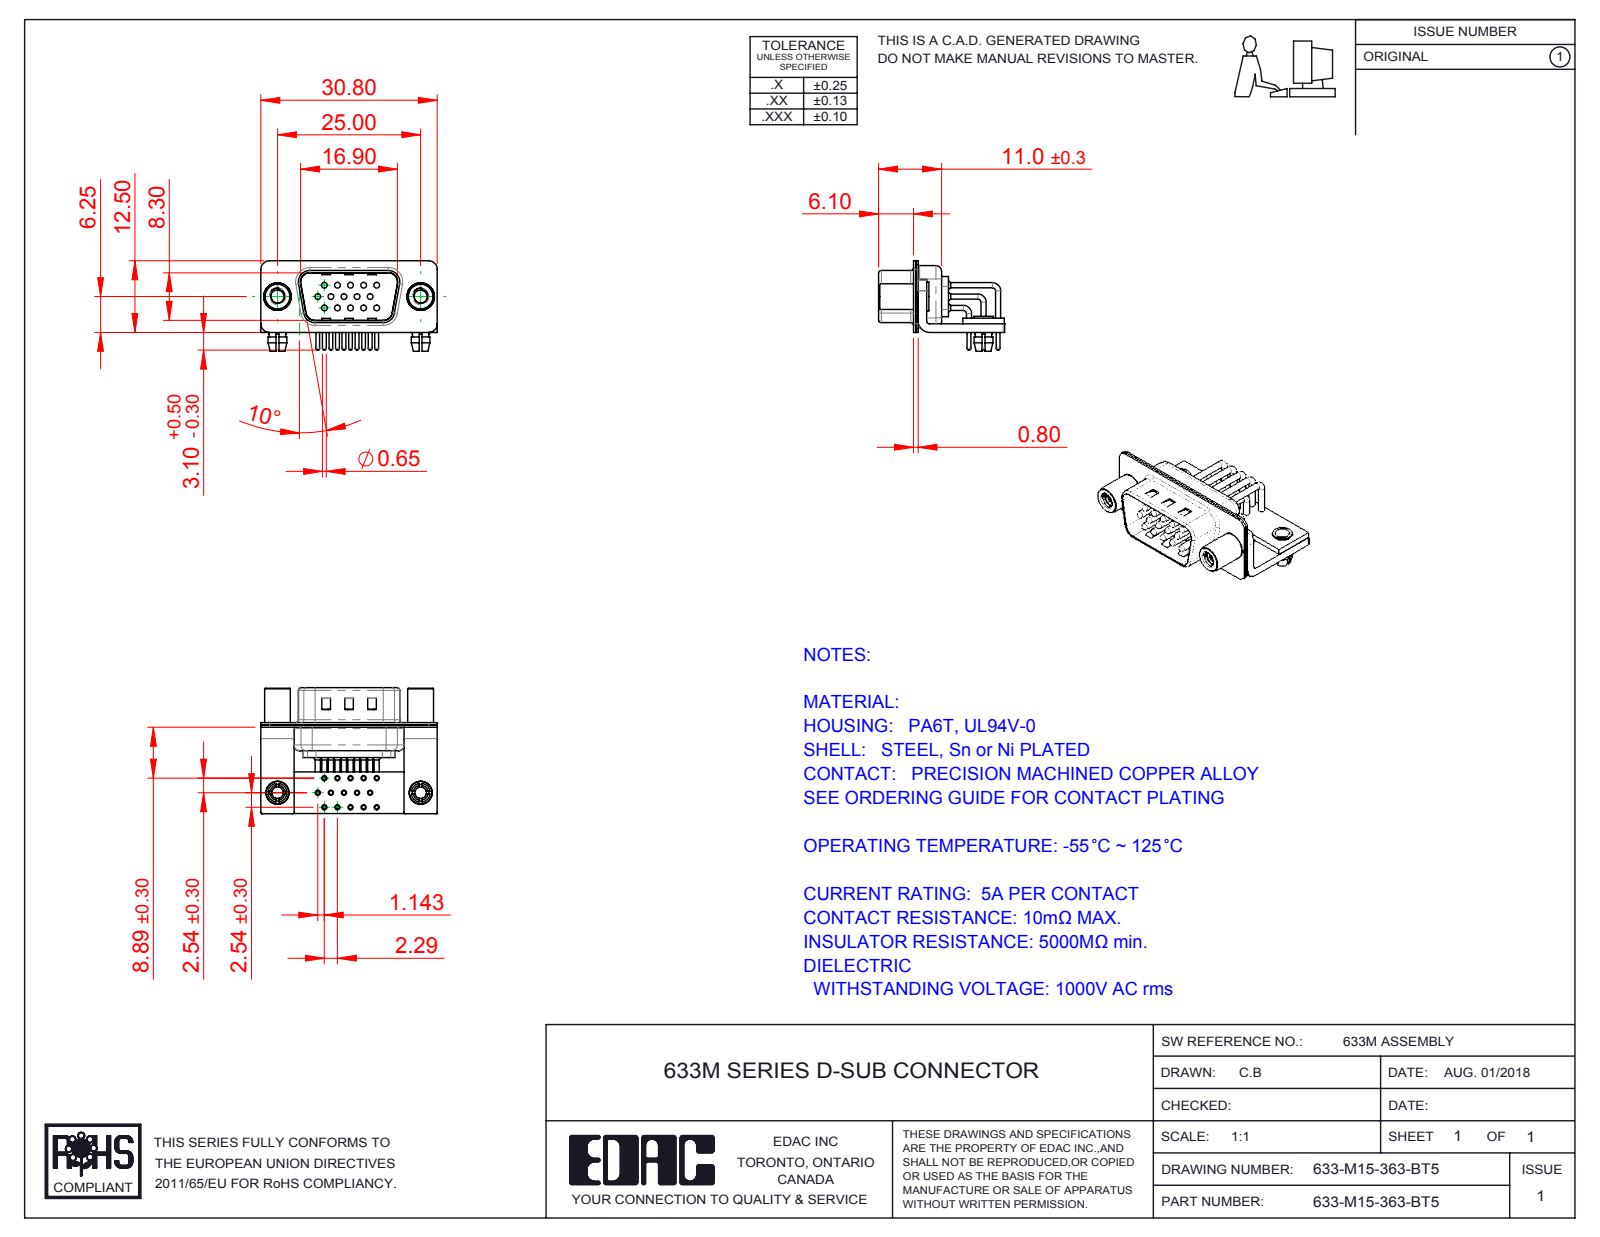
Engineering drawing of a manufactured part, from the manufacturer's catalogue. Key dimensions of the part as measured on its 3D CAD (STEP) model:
Part name (STEP PRODUCT): 633M Shell Front_15 Contacts; 633M Contact Row 3; 633M Shell Rear_15 Contacts; 633M Stabilizer Bracket (+7 more)
STEP written by: SolidWorks 2016 (CONFIG_CONTROL_DESIGN)
Units: millimetres
Bodies: 25 solids, 2176 faces (1143 planar, 795 cylindrical, 238 other)
Overall size (bounding box): 30.8 × 22 × 15.8
Volume: 2 100 mm³ · Surface area: 6 336 mm²
Round holes (diameter × count): ⌀2 ×17, ⌀0.9 ×15, ⌀1 ×15, ⌀1.7 ×15, ⌀2.26 ×2, ⌀2.5 ×2, ⌀3.2 ×2, ⌀4 ×2, ⌀4.8 ×2
Round bosses / shafts (diameter × count): ⌀0.9 ×16, ⌀1.5 ×15, ⌀0.65 ×15, ⌀5 ×2, ⌀4.9 ×2, ⌀4.5 ×2, ⌀4 ×2, ⌀3.4 ×2
Partial cylindrical surfaces — rounded edges, fillets, slot ends (radius × count): R0.25 ×16, R1.5 ×16, R1.01 ×15, R2 ×13, R0.5 ×9, R1.6 ×8, R0.6 ×4, R0.65 ×4
Main face-to-face distances: 0.4, 1.5, 0.8, 1, 0.85, 1.9, 2.5, 1.25, 10.4, 9.55
Hole centre spacings: 2.29, 4.57, 2.28, 3.96, 2.78, 4.27, 6.05, 6.86
